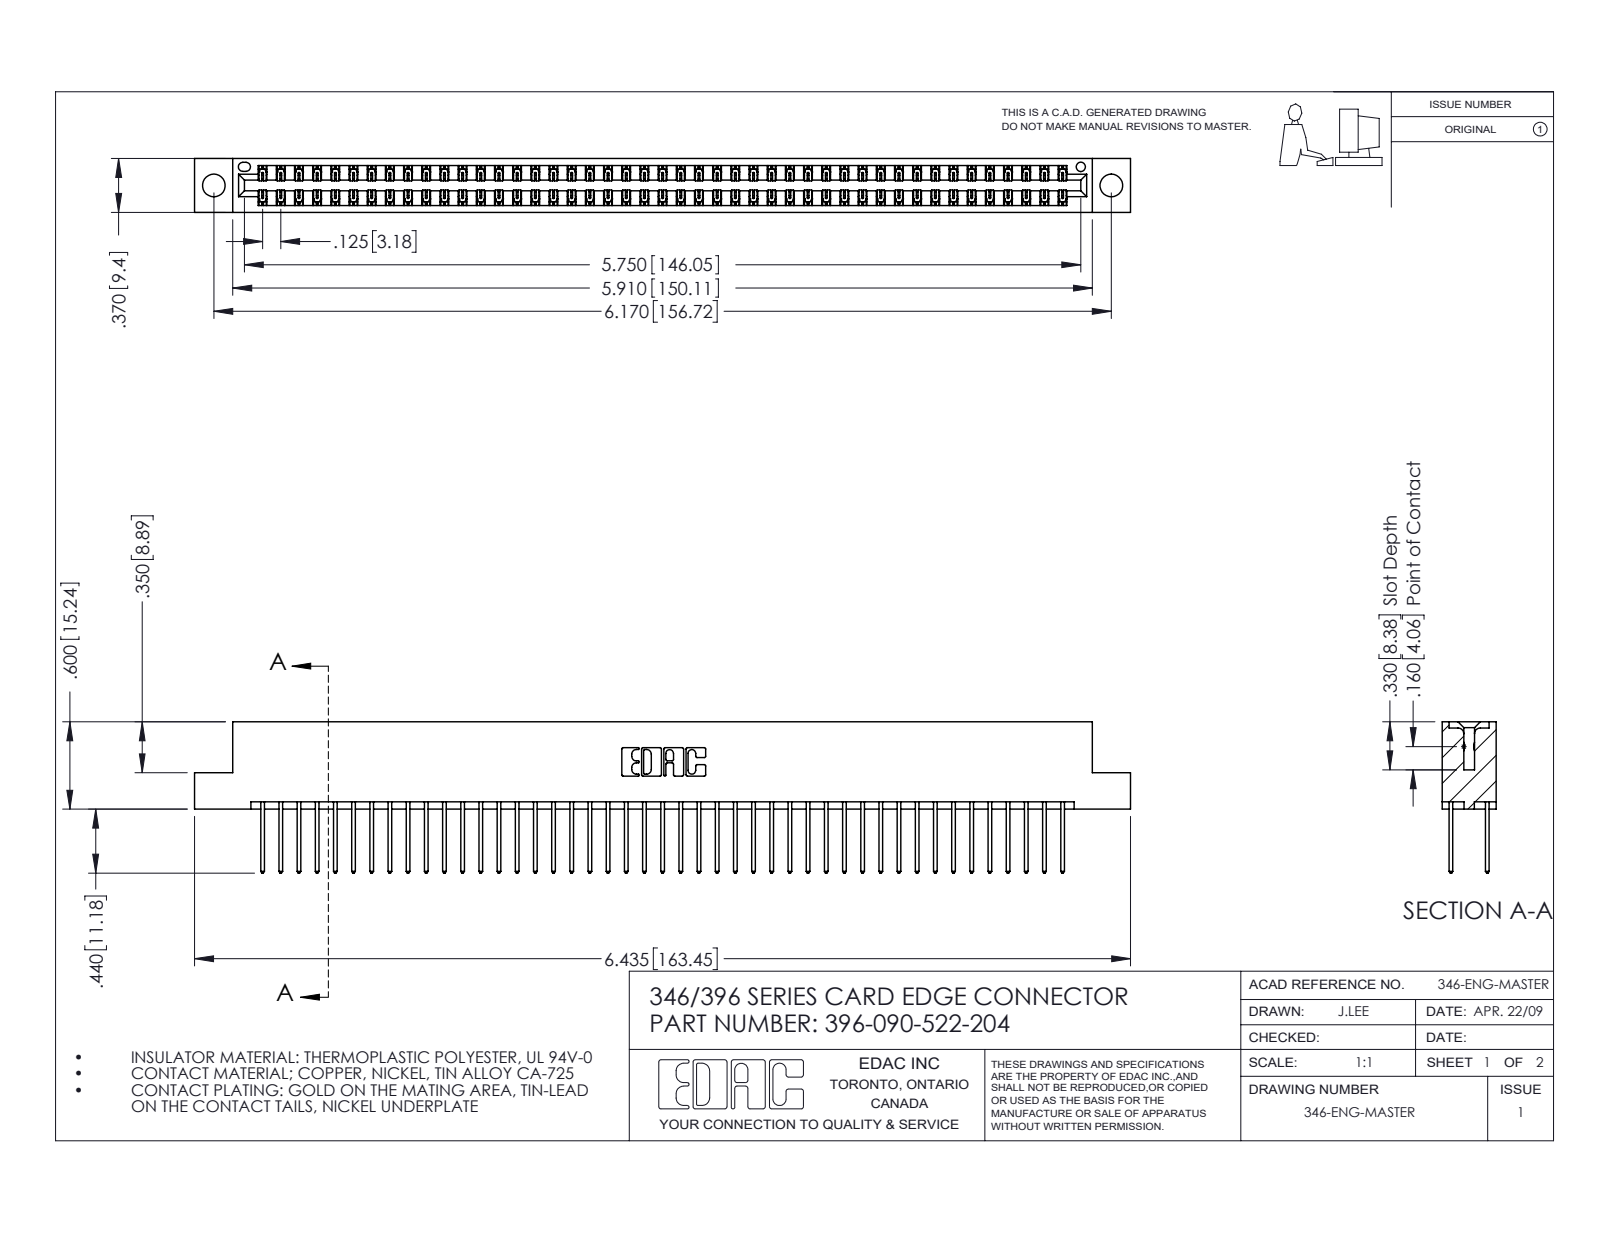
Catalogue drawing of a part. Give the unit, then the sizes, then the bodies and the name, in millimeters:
Units: millimetres
Overall size (bounding box): 163.4 × 26.4 × 9.4
Round holes (diameter × count): ⌀4 ×2, ⌀1.6 ×1
Partial cylindrical surfaces — rounded edges, fillets, slot ends (radius × count): R0.2 ×135, R0.3 ×90, R0.3 ×22, R0.2 ×6, R0.8 ×6, R0.7 ×3, R0.4 ×2, R0.6 ×2
Main face-to-face distances: 1.2, 8.2, 6.4, 9.4, 1.8, 7.6, 0.6, 7, 3.8, 5.6
Hole centre spacings: 6.2, 151.4, 156.7
Volume: 16 100 mm³ · Surface area: 23 060 mm²
Bodies: 91 solids, 4802 faces (3226 planar, 1576 cylindrical, 0 other)
Part name (STEP PRODUCT): 345-292-001_345-293-122; 346 Part_Flush Mounting Lugs - 0.156 Dia-TH; 396-090-522-204
STEP written by: SolidWorks 2016 (CONFIG_CONTROL_DESIGN)
